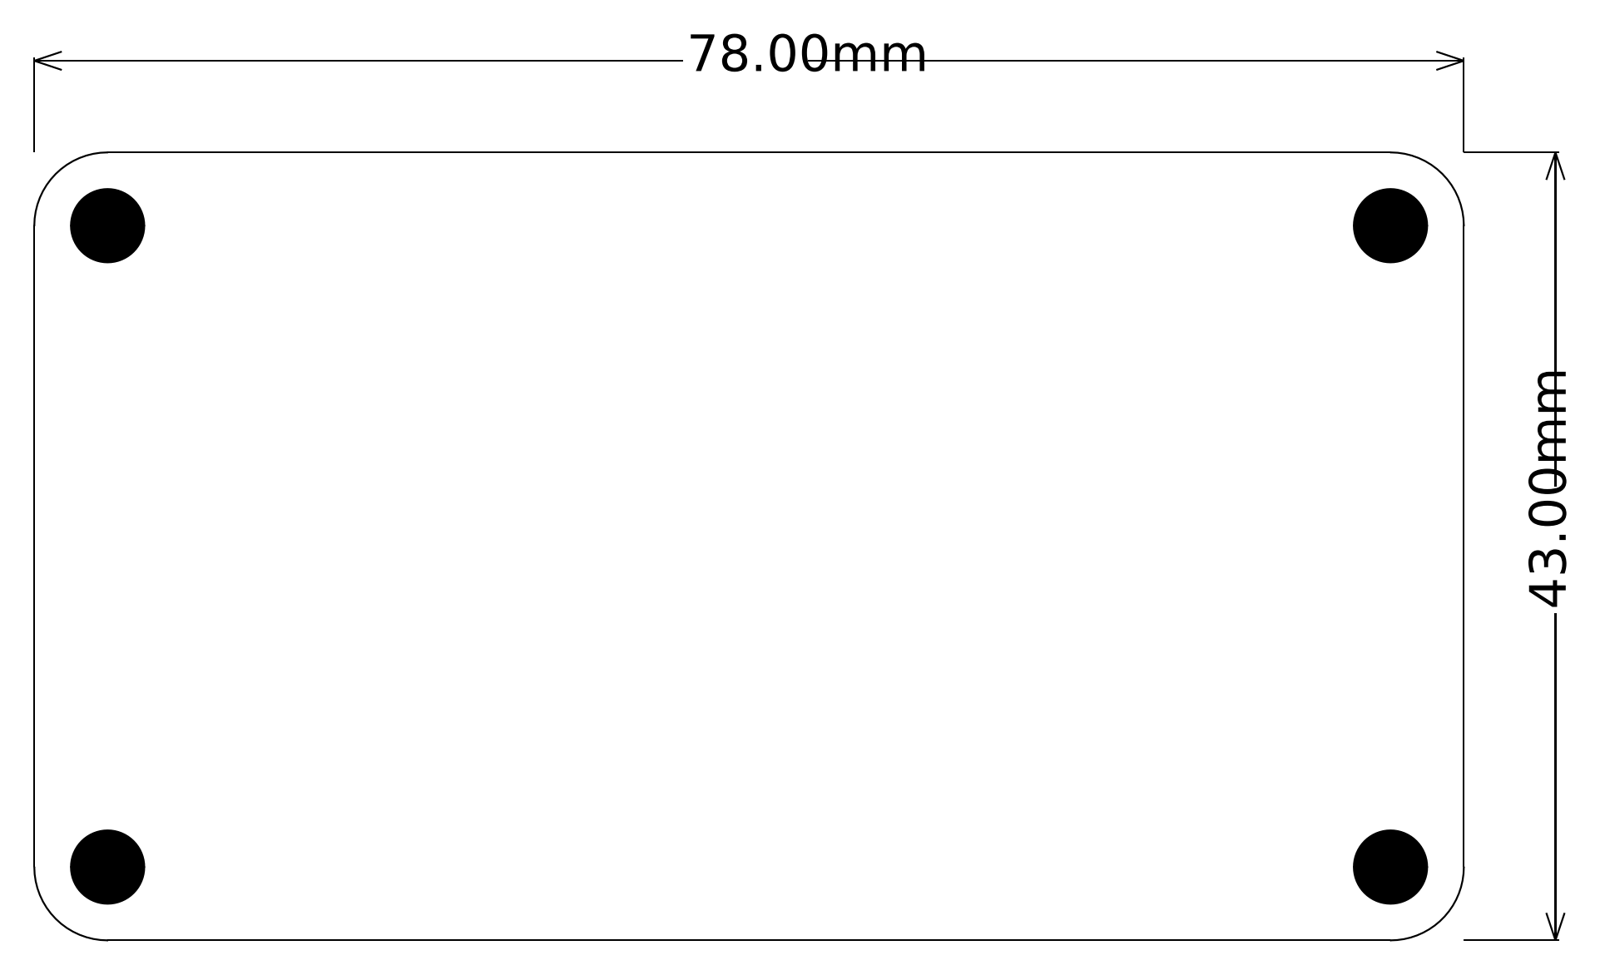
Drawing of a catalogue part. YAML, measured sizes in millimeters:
part_name: "PCB; Board"
step_written_by: "Open CASCADE 7.5 (AUTOMOTIVE_DESIGN)"
units: millimeters
bodies: {solids: 1, faces: 14, planar: 6, cylindrical: 8, other: 0}
overall_size: [78, 43, 1.6]
volume: 5264
surface_area: 7037
round_holes:
  - {diameter: 4, count: 4}
partial_cylinders:
  - {radius: 4, count: 4}
face_to_face_distances: [1.6, 43, 78]
hole_center_spacings: [35, 70, 78.26]
